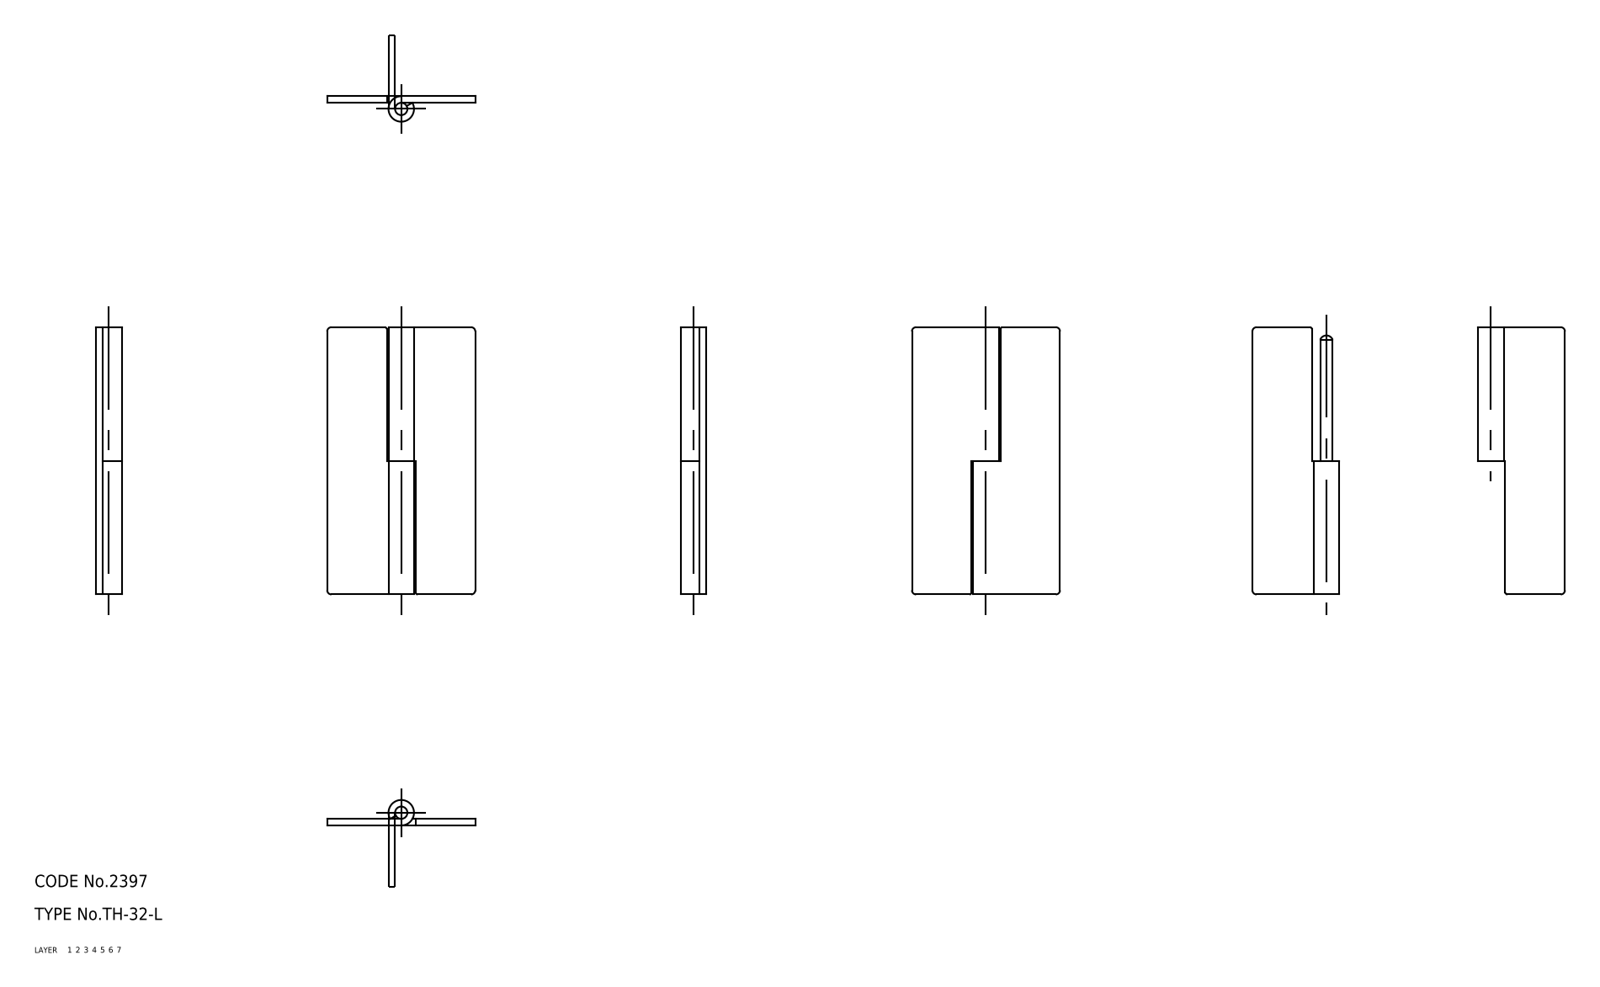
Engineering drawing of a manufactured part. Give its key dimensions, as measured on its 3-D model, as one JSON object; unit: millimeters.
{"part_name": "shaft; hinge piece_B; hinge piece_A; TH_32_L_7857_36", "step_written_by": "CADfix (AUTOMOTIVE_DESIGN)", "units": "millimeters", "bodies": {"solids": 3, "faces": 30, "planar": 0, "cylindrical": 0, "other": 30}, "overall_size": [65, 36, 6.2], "volume_mm3": 5066, "surface_area_mm2": 6984}
